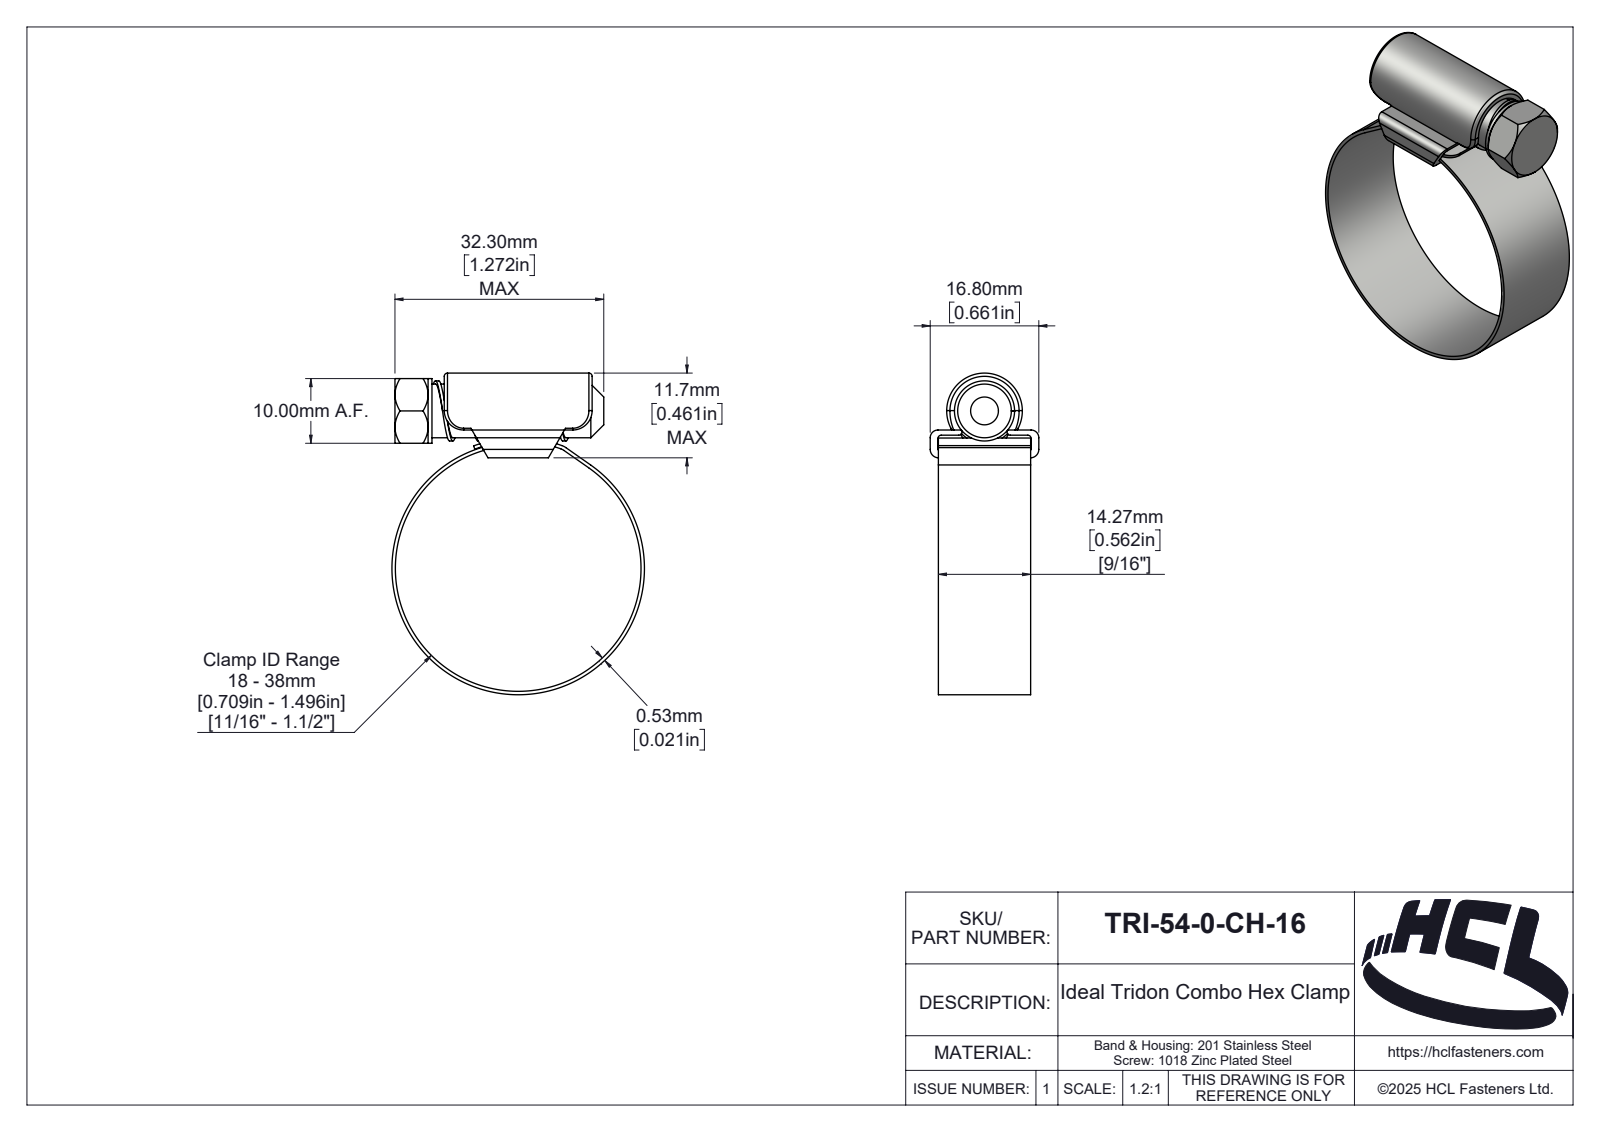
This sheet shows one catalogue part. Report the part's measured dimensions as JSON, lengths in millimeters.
{"part_name": "TRI-54-0-CH-16", "step_written_by": "SolidWorks 2025 (AUTOMOTIVE_DESIGN)", "units": "millimeters", "bodies": {"solids": 3, "faces": 212, "planar": 35, "cylindrical": 101, "other": 76}, "overall_size": [49.73, 39.06, 16.8], "volume_mm3": 3855, "surface_area_mm2": 6781, "round_holes": [[38, 1]], "round_bosses_or_shafts": [[39.06, 1], [10, 1], [8.3, 1]], "partial_cylinders_radius": [[0.5, 6], [3, 4], [0.1, 2], [1.2, 2], [1.3, 2], [0.46, 1], [1.89, 1], [2, 1]], "face_to_face_distances": [1.2, 3.5, 2.3, 4.3, 3.1, 0.8, 0.53, 14.26, 9.99, 1.27]}
